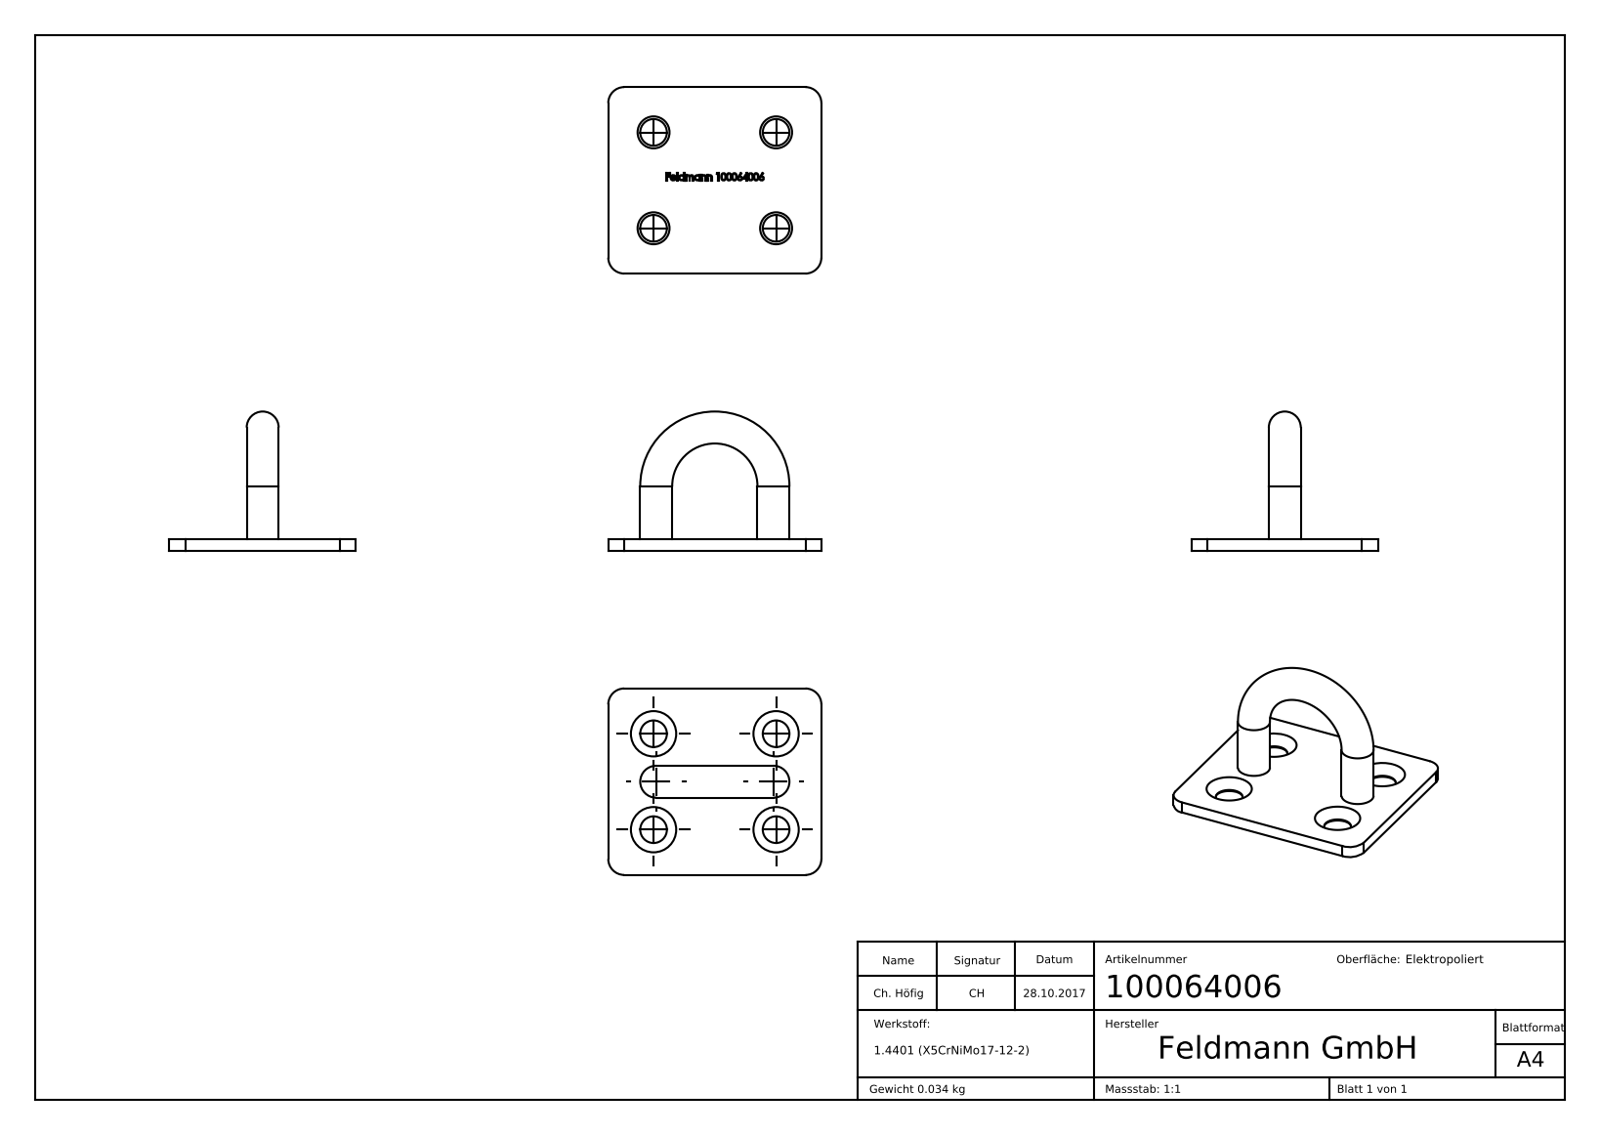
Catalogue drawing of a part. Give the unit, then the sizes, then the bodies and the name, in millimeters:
Units: millimetres
Overall size (bounding box): 40 × 35 × 26.2
Round bosses / shafts (diameter × count): ⌀6 ×2
Partial cylindrical surfaces — rounded edges, fillets, slot ends (radius × count): R3 ×4
Main face-to-face distances: 2.2, 35, 40, 2.1, 17.5, 0.39, 2.02, 1.26, 12.99, 1.65
Volume: 4 310 mm³ · Surface area: 4 005 mm²
Bodies: 1 solid, 250 faces (113 planar, 8 cylindrical, 129 other)
Part name (STEP PRODUCT): 100064006
STEP written by: SolidWorks 2015 (CONFIG_CONTROL_DESIGN)
